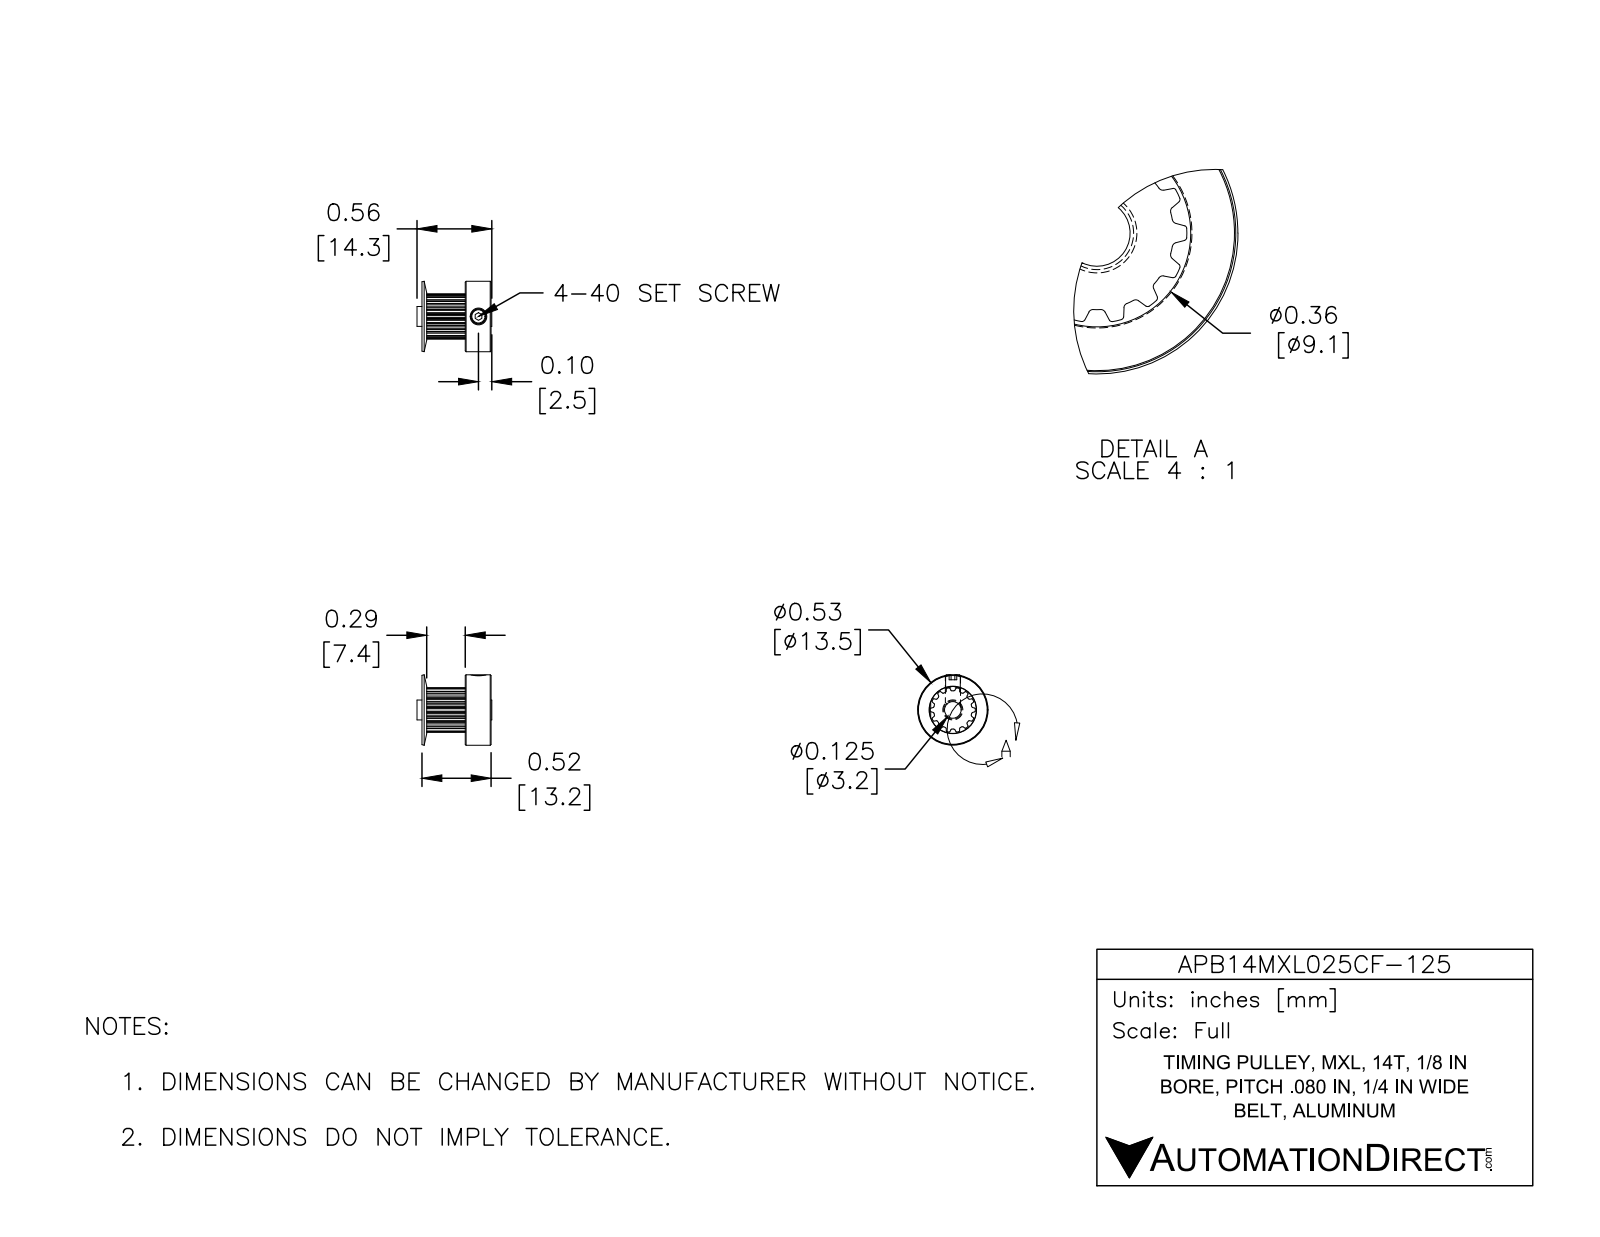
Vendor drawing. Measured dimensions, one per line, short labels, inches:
name: APB14MXL025CF-125
written by: SolidWorks 2016 (AUTOMOTIVE_DESIGN)
unit: in
bodies: 2 solids, 166 faces (43 planar, 105 cylindrical, 18 other)
size: 0.563 × 0.53 × 0.53
volume: 0.062 in³; area: 1.806 in²
holes: 1× ⌀0.114, 1× ⌀0.125
bosses: 1× ⌀0.53, 1× ⌀0.15, 1× ⌀0.11
rounds: 28× R0.005, 28× R0.009, 1× R0.144, 1× R0.169
face distances: 0.194, 0.309, 0.504, 0.113, 0.019, 0.29, 0.485, 0.098, 0.05, 0.508
